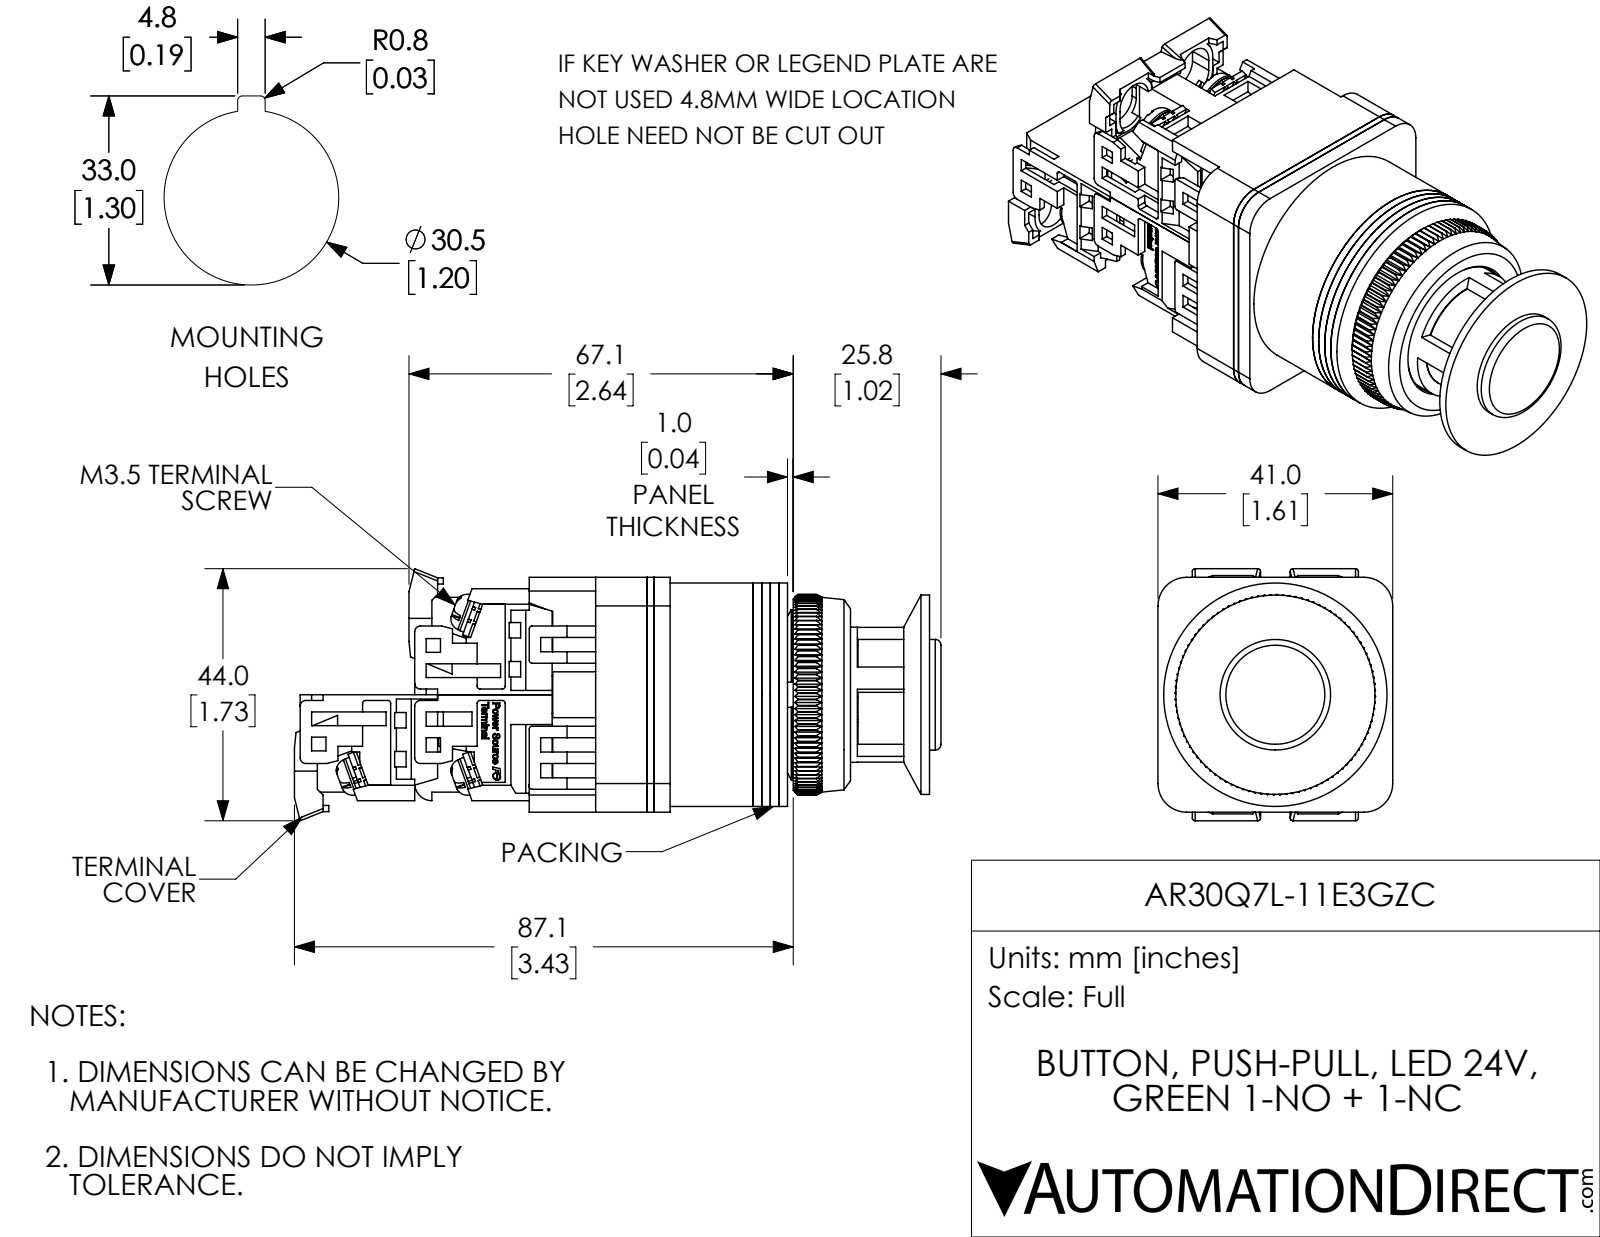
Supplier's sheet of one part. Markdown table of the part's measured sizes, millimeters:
| quantity | value |
| --- | --- |
| part name | AR30Q7L-11E3GZC |
| STEP written by | SolidWorks 2017 (AUTOMOTIVE_DESIGN) |
| units | millimeters |
| bodies | 34 solids, 2350 faces (1693 planar, 341 cylindrical, 316 other) |
| overall size | 112.9 × 44 × 41 |
| volume | 80 000 mm³ |
| surface area | 57 600 mm² |
| round holes (diameter × count) | 3.5 × 8, 3.6 × 6, 5.5 × 1, 8.5 × 1, 11.5 × 1, 14.5 × 1, 17 × 1, 17.3 × 1, 19.3 × 1, 19.5 × 1, 24 × 1, 24.5 × 1 |
| round bosses / shafts (diameter × count) | 6.6 × 6, 3.5 × 6, 39 × 1, 34.8 × 1, 30 × 1, 27.6 × 1, 23.6 × 1, 21 × 1 |
| partial cylindrical surfaces (radius × count) | 1.5 × 24, 0.5 × 20, 1 × 6, 3.5 × 4, 4.5 × 4, 5 × 4, 3 × 3, 17.5 × 1 |
| main face-to-face distances | 1.5, 1.2, 3, 20, 21.8, 4.5, 20.5, 17.3, 1.6, 18.8 |
| hole center spacings | 14.7, 16.2, 6.8, 6.8 |
